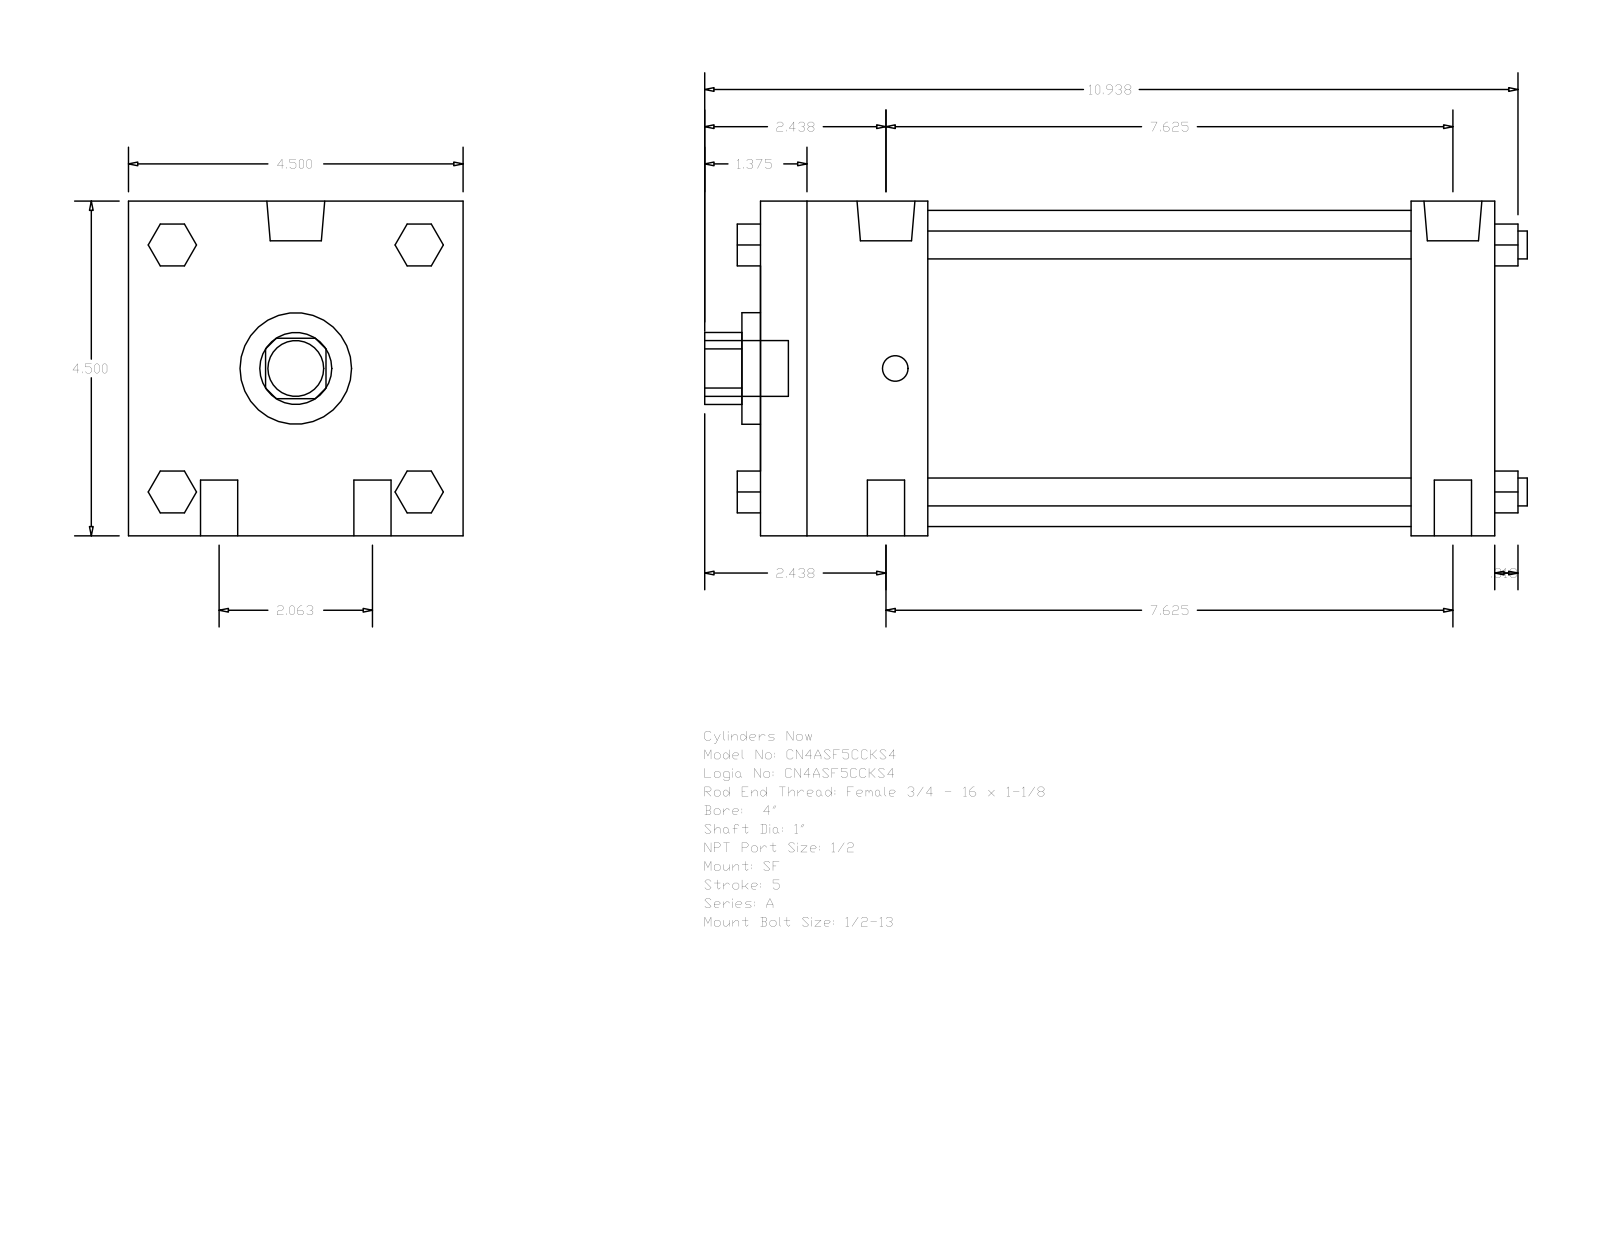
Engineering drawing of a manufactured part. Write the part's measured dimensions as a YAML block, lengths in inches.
part_name: "A_SF__0400_1"
step_written_by: "GSSL Pune (CONFIG_CONTROL_DESIGN)"
units: inches
bodies: {solids: 0, faces: 124, planar: 94, cylindrical: 30, other: 0}
overall_size: [11.063, 4.5, 4.5]
round_holes:
  - {diameter: 1, count: 1}
  - {diameter: 1.5, count: 1}
  - {diameter: 4.25, count: 1}
round_bosses_or_shafts:
  - {diameter: 0.5, count: 4}
  - {diameter: 0.375, count: 4}
  - {diameter: 0.778, count: 2}
  - {diameter: 0.344, count: 2}
  - {diameter: 0.75, count: 1}
partial_cylinders:
  - {radius: 0.484, count: 1}
face_to_face_distances: [4.5, 9.875, 8.75, 1.125, 2.25, 6.5, 7.625, 0.563, 1.66, 2.875]
